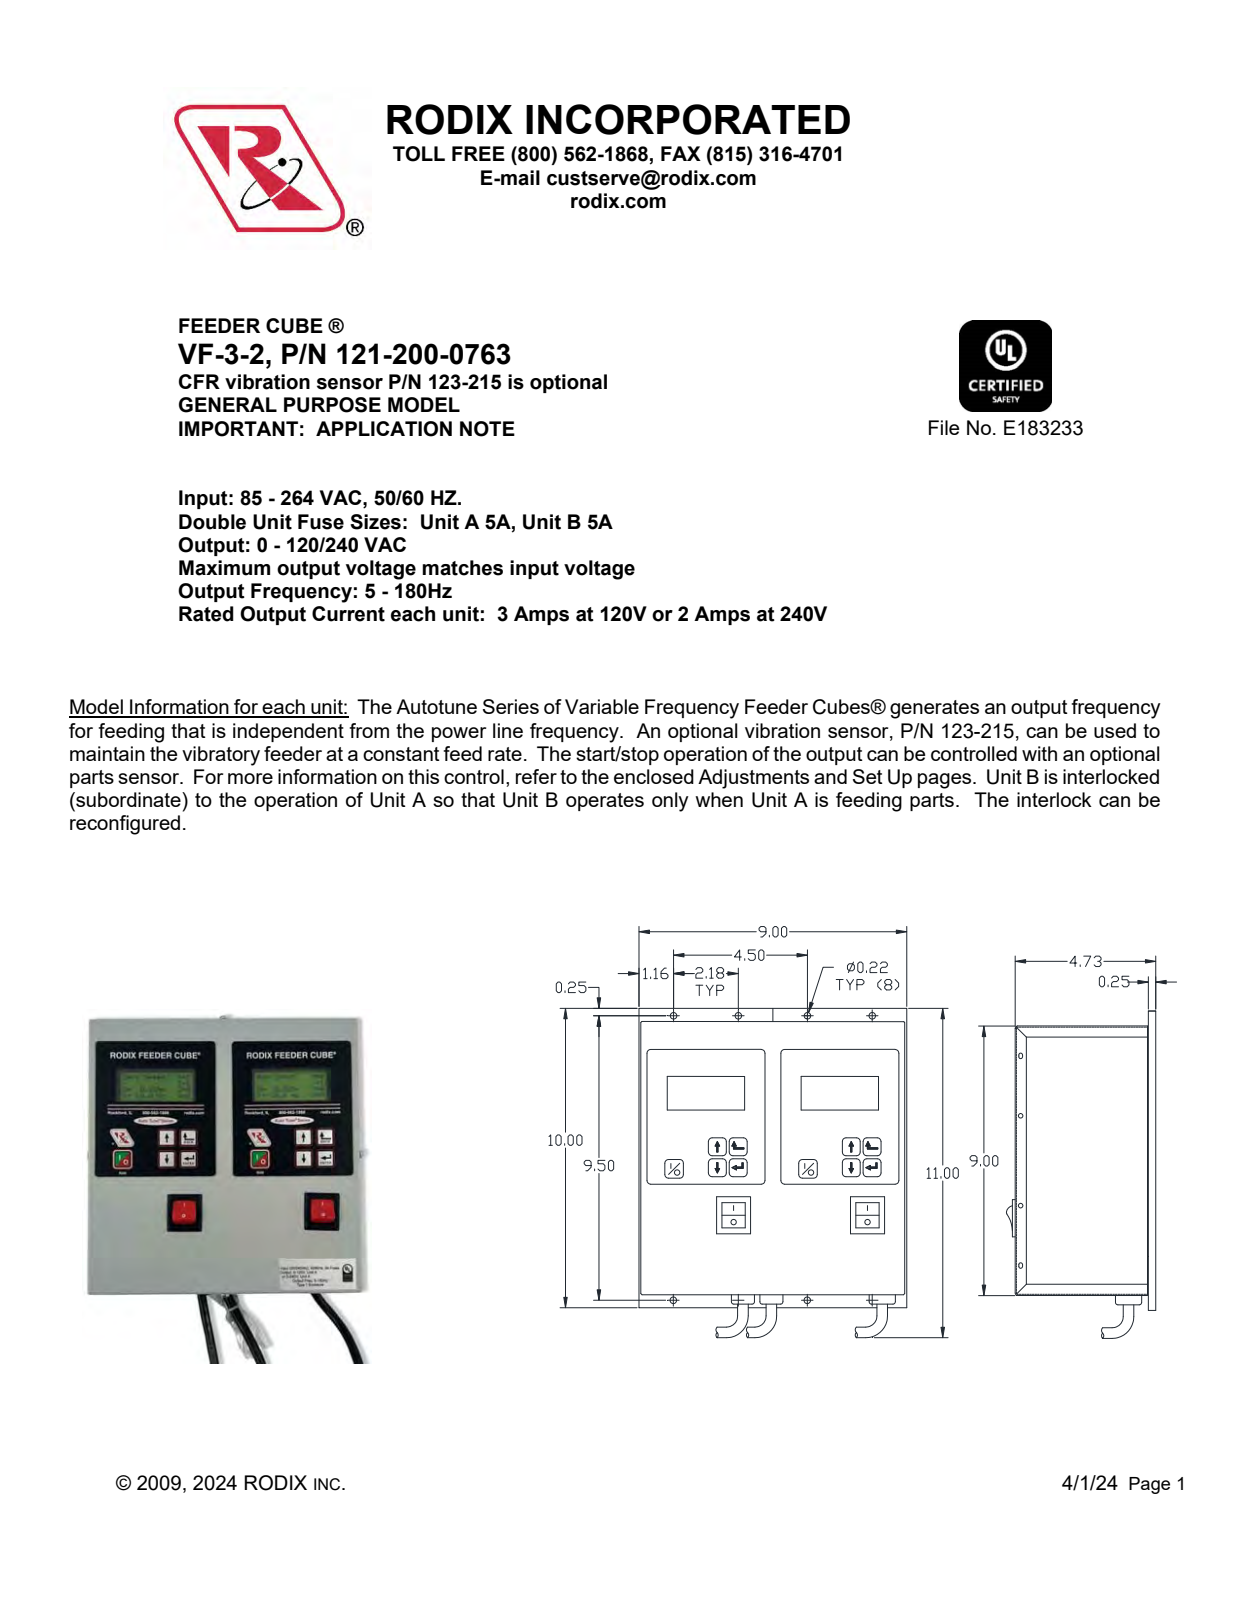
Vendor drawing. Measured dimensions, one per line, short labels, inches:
name: CABLE CLAMP_DEFAULT; 112-000-0312_DEFAULT; 121-200-0763; 112-000-0310_DEFAULT (+8 more)
written by: SolidWorks 2022 (AUTOMOTIVE_DESIGN)
unit: in
bodies: 25 solids, 3279 faces (1961 planar, 437 cylindrical, 881 other)
size: 10.888 × 9.118 × 5
volume: 40.48 in³; area: 853.3 in²
holes: 12× ⌀0.17, 10× ⌀0.107, 8× ⌀0.136, 8× ⌀0.221, 5× ⌀0.101, 5× ⌀0.141, 4× ⌀0.15, 4× ⌀0.375, 3× ⌀0.375, 3× ⌀0.437, 2× ⌀0.118, 1× ⌀0.08
bosses: 4× ⌀0.61, 4× ⌀0.5, 4× ⌀0.355, 3× ⌀0.56, 3× ⌀0.43, 2× ⌀0.14, 2× ⌀0.034
rounds: 40× R0.1, 36× R0.05, 34× R0.065, 18× R0.125, 12× R0.062, 8× R0.03, 8× R0.034, 8× R0.064
face distances: 0.051, 4.55, 0.051, 0.25, 4.8, 4.749, 4.499, 9.016, 8.965, 8.914
hole spacings: 0.82, 1.464, 1.801, 2.182, 2.727, 2.919, 3.228, 3.25
